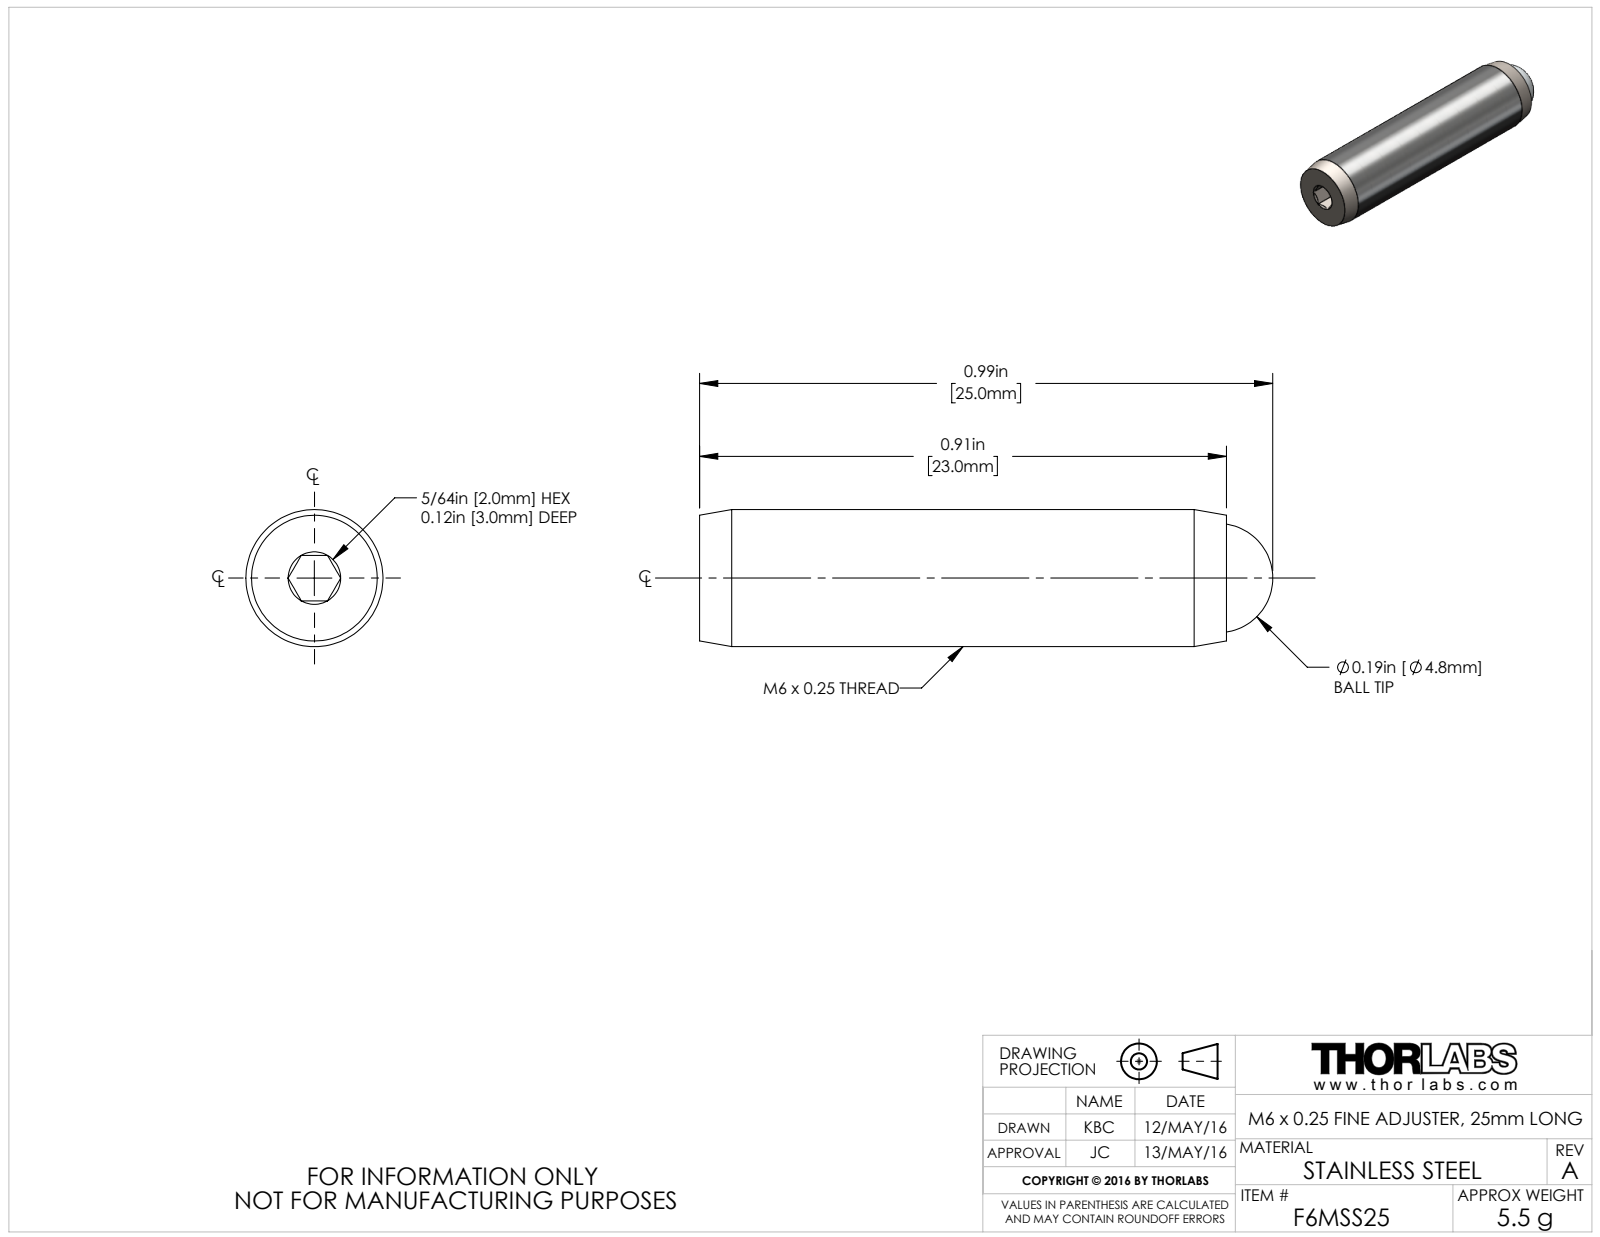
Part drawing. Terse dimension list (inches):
name: TTN102530-E0W
written by: SolidWorks 2016 (CONFIG_CONTROL_DESIGN)
unit: in
bodies: 2 solids, 27 faces (9 planar, 4 cylindrical, 14 other)
size: 0.985 × 0.235 × 0.235
volume: 0.04 in³; area: 0.925 in²
holes: 1× ⌀0.188
bosses: 1× ⌀0.235
face distances: 0.078, 0.906, 0.12, 0.785
